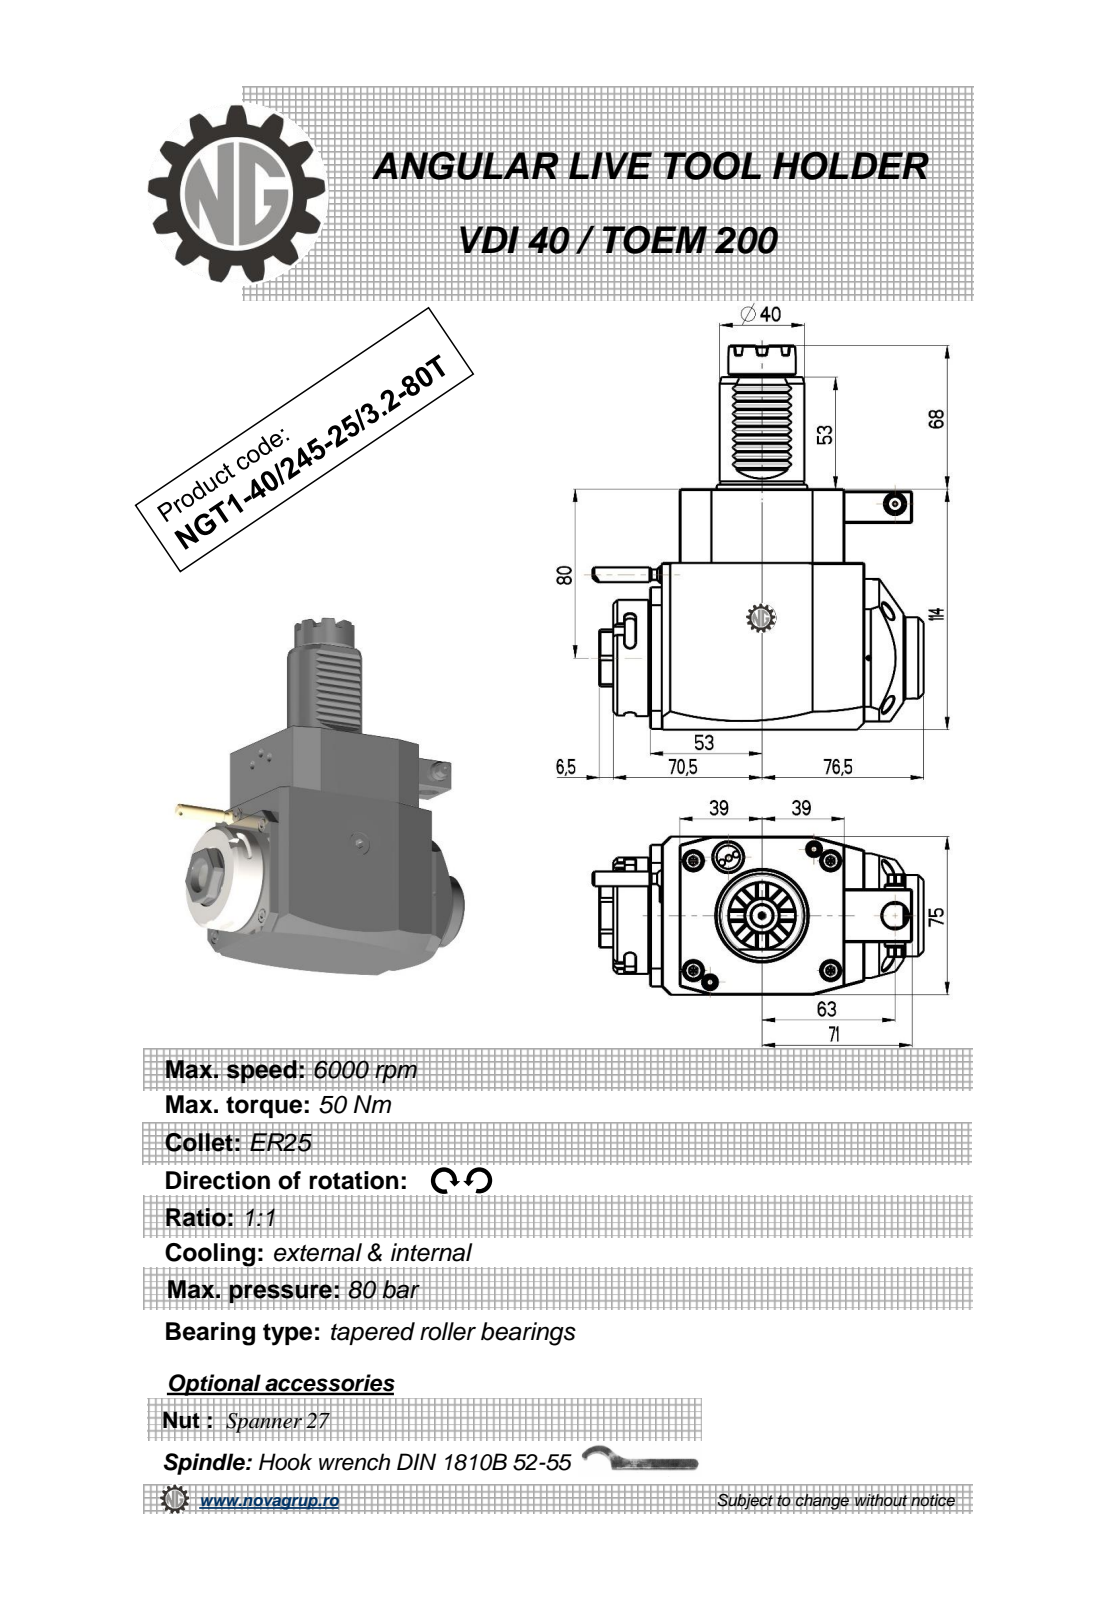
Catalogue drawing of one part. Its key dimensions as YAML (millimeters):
part_name: "NGT1_40_245_25_3_2_80T"
step_written_by: "PRO/ENGINEER BY PARAMETRIC TECHNOLOGY CORPORATION, 2010280 (CONFIG_CONTROL_DESIGN)"
units: millimeters
bodies: {solids: 1, faces: 423, planar: 221, cylindrical: 88, other: 114}
overall_size: [182, 156.83, 75]
volume: 966621
surface_area: 72856
round_holes:
  - {diameter: 2, count: 1}
  - {diameter: 2.5, count: 1}
  - {diameter: 3, count: 1}
  - {diameter: 9.5, count: 1}
  - {diameter: 12, count: 1}
  - {diameter: 18, count: 1}
round_bosses_or_shafts:
  - {diameter: 8, count: 2}
  - {diameter: 55, count: 1}
  - {diameter: 48, count: 1}
  - {diameter: 40, count: 1}
  - {diameter: 38.5, count: 1}
  - {diameter: 32, count: 1}
  - {diameter: 17.2, count: 1}
  - {diameter: 10, count: 1}
partial_cylinders:
  - {radius: 0.3, count: 10}
  - {radius: 2.5, count: 6}
  - {radius: 180, count: 2}
  - {radius: 0.5, count: 1}
  - {radius: 3.85, count: 1}
  - {radius: 4.25, count: 1}
  - {radius: 15, count: 1}
  - {radius: 24.5, count: 1}
face_to_face_distances: [75, 114, 14, 17.5, 92, 78, 31.5, 109.5, 35, 4]
hole_center_spacings: [37.35, 43.2, 72.5]
